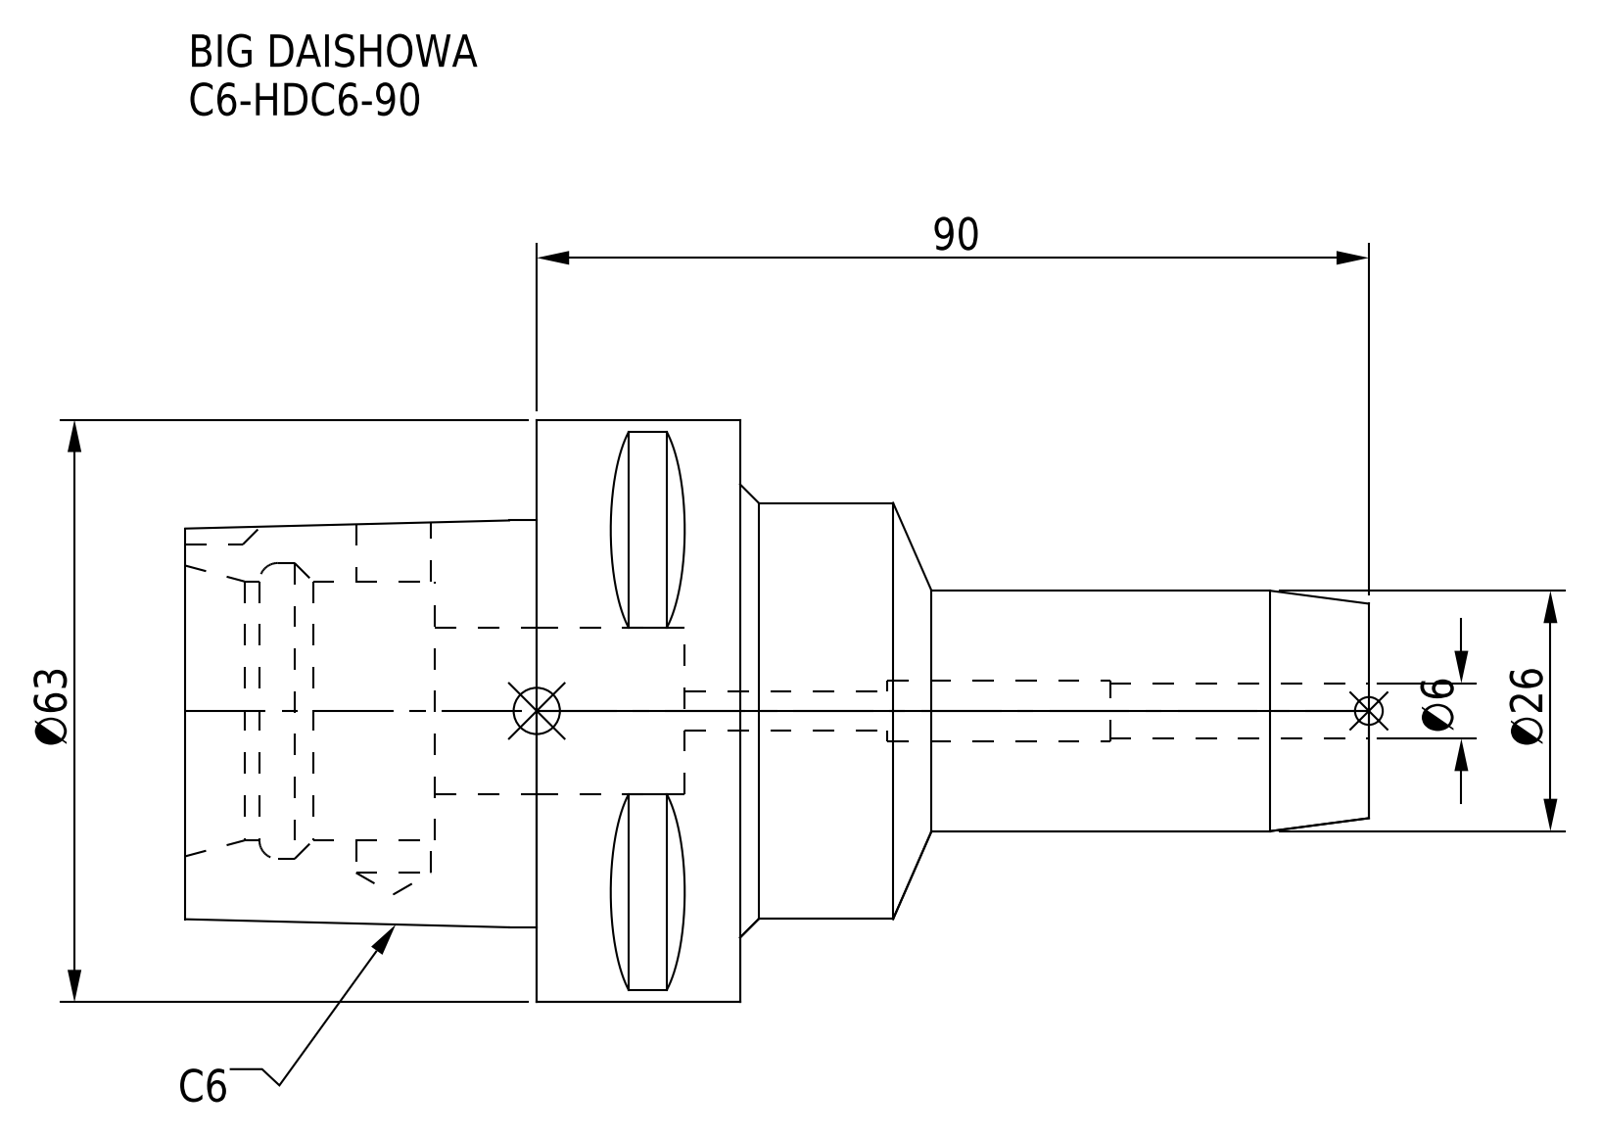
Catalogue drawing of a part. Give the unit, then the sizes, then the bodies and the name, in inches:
Units: inches
Overall size (bounding box): 5.039 × 2.48 × 2.48
Round holes (diameter × count): ⌀0.165 ×1, ⌀0.236 ×1, ⌀0.256 ×1, ⌀0.319 ×1, ⌀0.709 ×1, ⌀1.102 ×1, ⌀1.26 ×1
Round bosses / shafts (diameter × count): ⌀2.48 ×1, ⌀1.772 ×1, ⌀1.024 ×1
Partial cylindrical surfaces — rounded edges, fillets, slot ends (radius × count): R0.197 ×1
Main face-to-face distances: 0.866, 1.063, 2.362, 1.496, 2.677, 3.543, 5.039, 3.976, 1.299, 0.433
Volume: 9.155 in³ · Surface area: 42.52 in²
Bodies: 1 solid, 71 faces (30 planar, 25 cylindrical, 16 other)
Part name (STEP PRODUCT): C6-HDC6-90
STEP written by: CREO PARAMETRIC BY PTC INC, 2016380 (AUTOMOTIVE_DESIGN)
